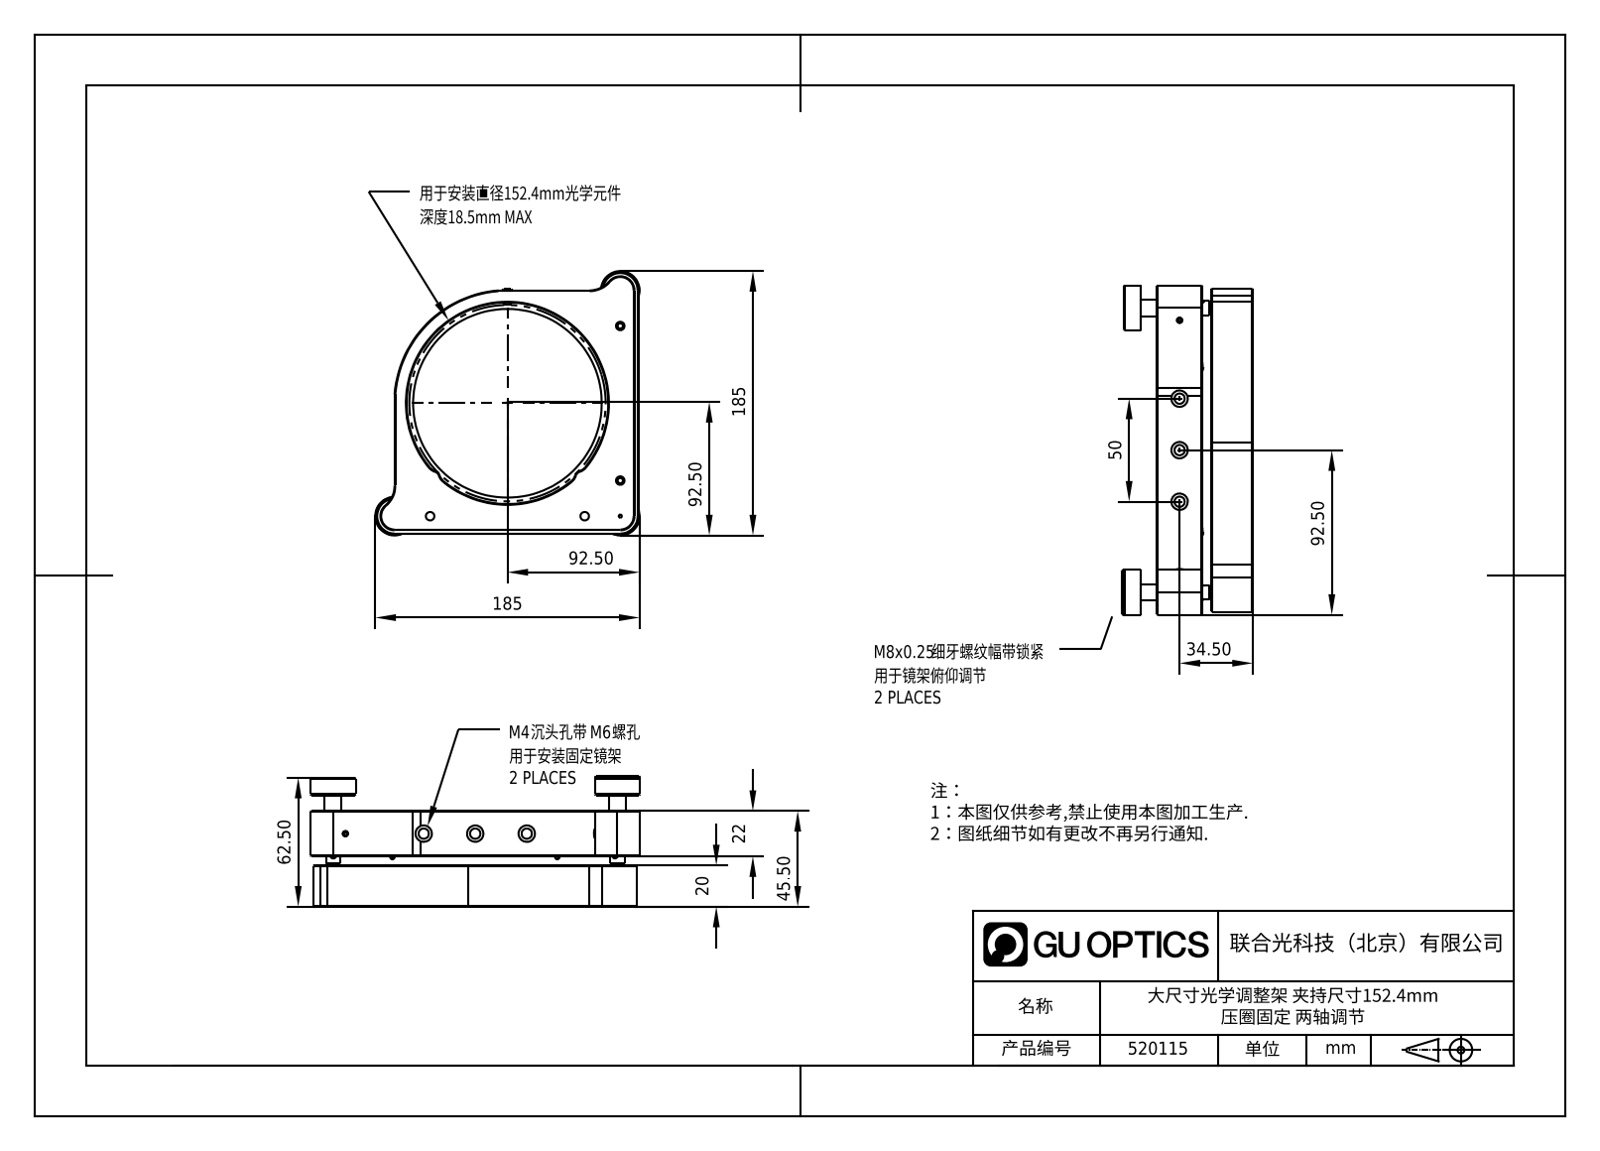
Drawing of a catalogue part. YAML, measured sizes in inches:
step_written_by: "SolidWorks 2021 (CONFIG_CONTROL_DESIGN)"
units: inches
bodies: {solids: 0, faces: 362, planar: 102, cylindrical: 176, other: 84}
overall_size: [7.283, 7.283, 2.461]
round_holes:
  - {diameter: 0.315, count: 12}
  - {diameter: 0.13, count: 6}
  - {diameter: 0.197, count: 6}
  - {diameter: 0.472, count: 3}
  - {diameter: 0.059, count: 2}
  - {diameter: 0.098, count: 2}
  - {diameter: 0.236, count: 2}
  - {diameter: 0.047, count: 1}
  - {diameter: 5.748, count: 1}
  - {diameter: 5.803, count: 1}
  - {diameter: 6, count: 1}
  - {diameter: 6.039, count: 1}
round_bosses_or_shafts:
  - {diameter: 0.079, count: 6}
  - {diameter: 0.866, count: 2}
  - {diameter: 0.315, count: 2}
  - {diameter: 0.5, count: 1}
partial_cylinders:
  - {radius: 0.041, count: 12}
  - {radius: 0.118, count: 8}
  - {radius: 0.236, count: 4}
  - {radius: 0.374, count: 3}
  - {radius: 0.984, count: 2}
  - {radius: 1.102, count: 2}
  - {radius: 1.181, count: 2}
  - {radius: 0.433, count: 1}
face_to_face_distances: [0.787, 0.866, 0.138, 0.059, 0.925, 1.004, 1.791, 0.65, 0.591, 0.63]
hole_center_spacings: [0.984, 4.538, 0.846, 1.181, 1.831, 1.969, 1.988, 2.972]
